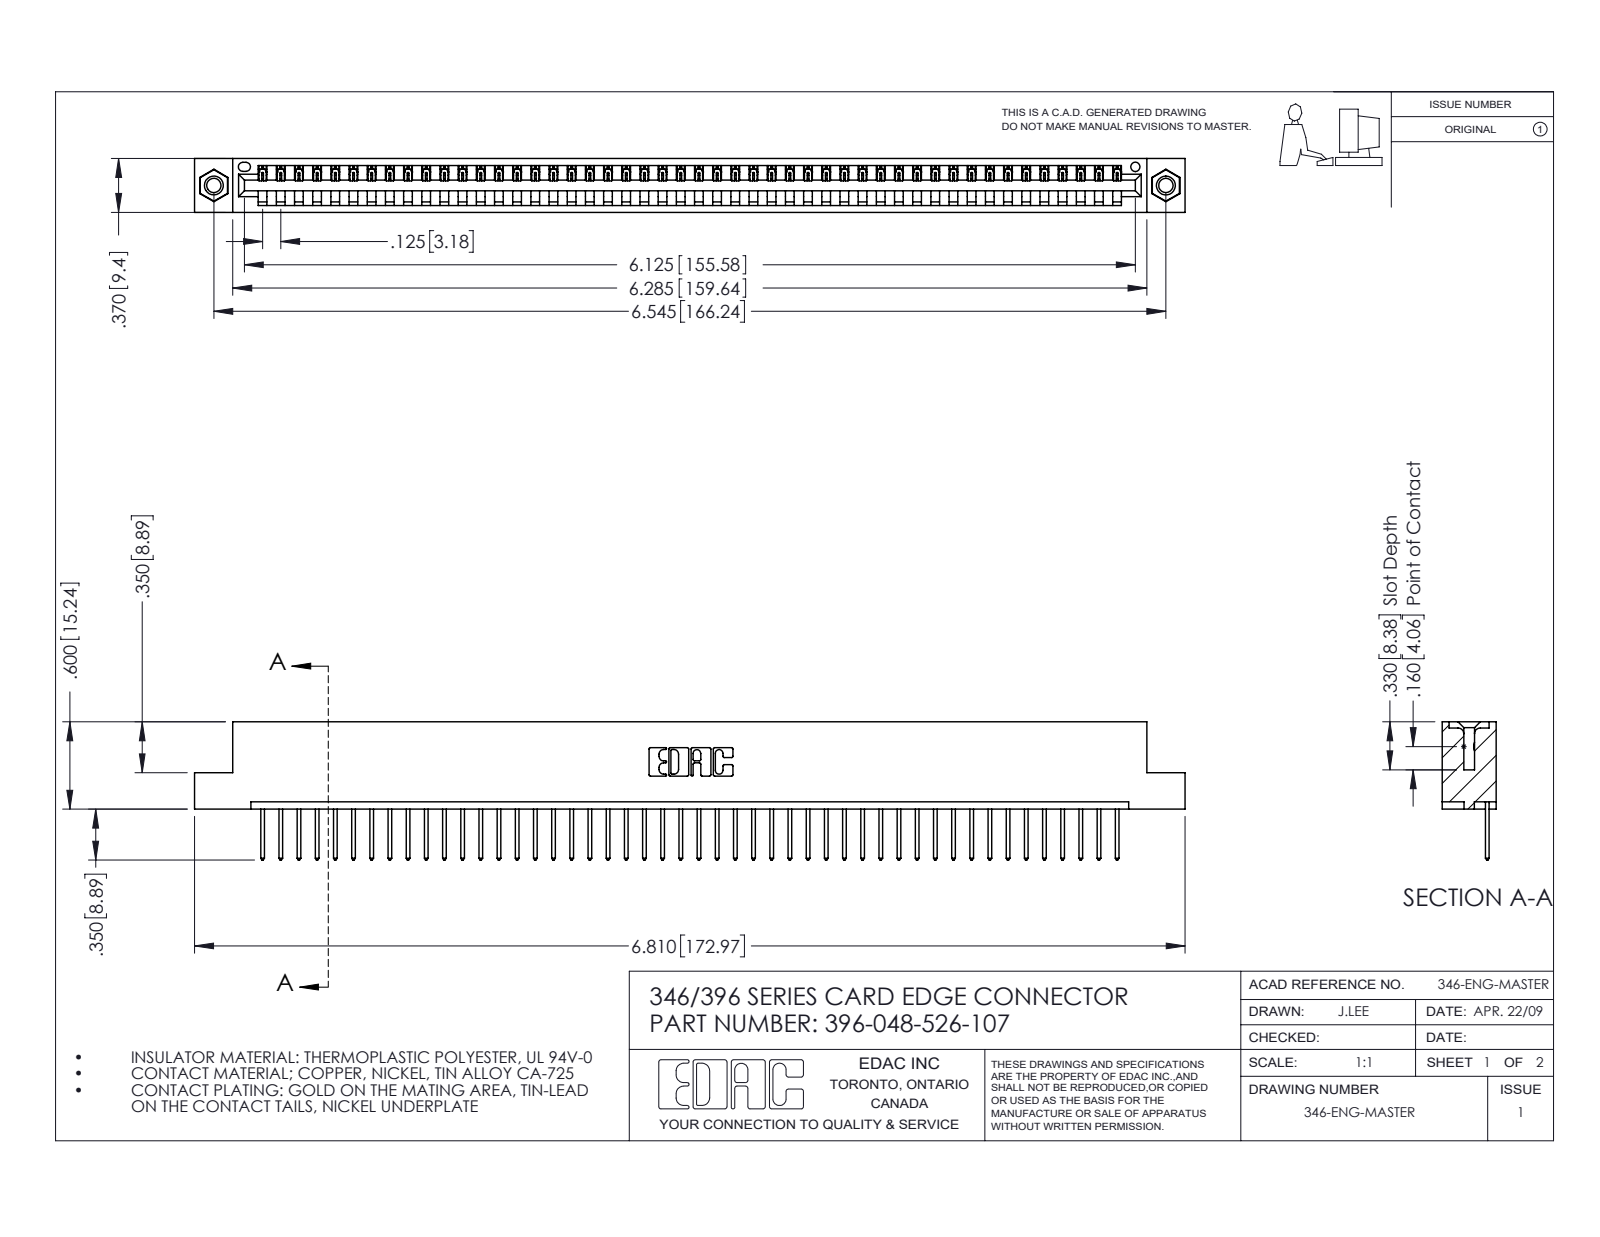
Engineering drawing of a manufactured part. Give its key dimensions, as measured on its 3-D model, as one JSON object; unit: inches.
{"part_name": "345-292-001_345-293-126; 345-250-001_345-250-005-103; 346 Part_Flush Mounting Lugs - 0.156 Dia-TI; 396-048-526-107", "step_written_by": "SolidWorks 2016 (CONFIG_CONTROL_DESIGN)", "units": "inches", "bodies": {"solids": 51, "faces": 2966, "planar": 2028, "cylindrical": 922, "other": 16}, "overall_size": [6.81, 0.95, 0.37], "volume_in3": 1.01, "surface_area_in2": 32.14, "round_holes": [[0.098, 2], [0.125, 2], [0.156, 2], [0.064, 1]], "round_bosses_or_shafts": [[0.155, 2]], "partial_cylinders_radius": [[0.006, 96], [0.01, 96], [0.01, 22], [0.007, 6], [0.031, 6], [0.026, 3], [0.031, 2], [0.04, 2]], "face_to_face_distances": [0.048, 0.322, 0.37, 0.25, 0.072, 0.298, 0.025, 0.148, 0.222, 0.1], "hole_center_spacings": [0.246, 6.336, 6.545]}
